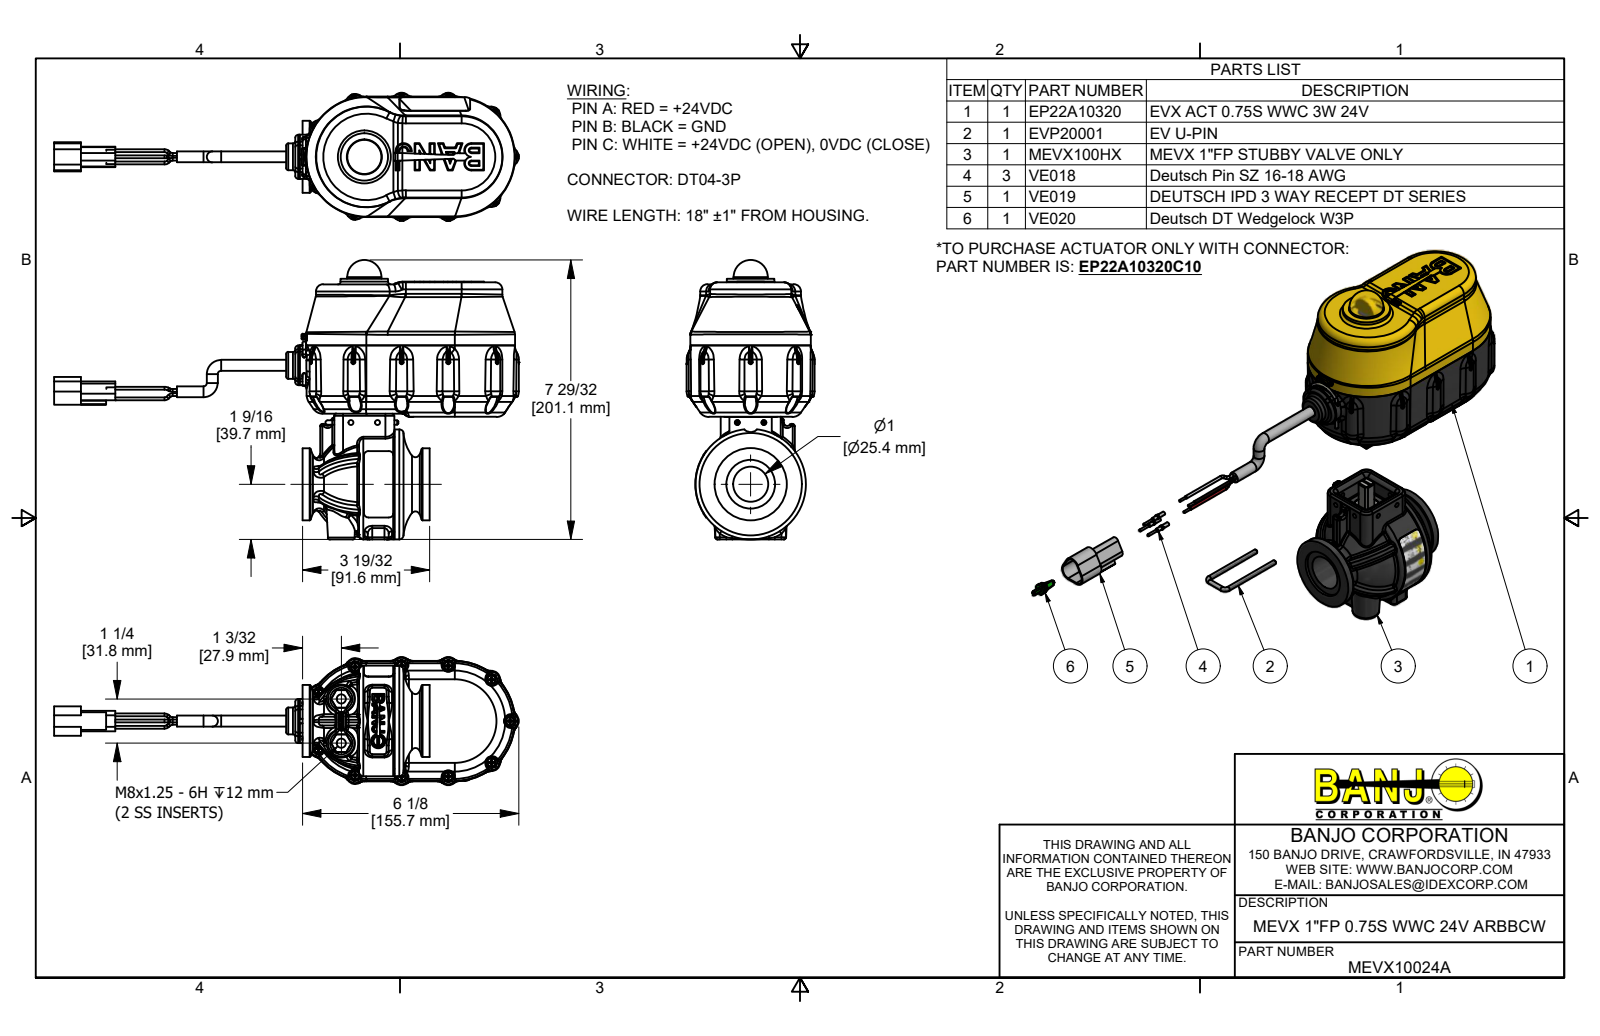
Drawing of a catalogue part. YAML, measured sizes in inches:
part_name: "MEVX10024A; EVP20001; MEVX100HX; MEVPS10254H (+8 more)"
step_written_by: "Autodesk Inventor 2019 (AUTOMOTIVE_DESIGN)"
units: inches
bodies: {solids: 89, faces: 11108, planar: 3083, cylindrical: 3143, other: 4882}
overall_size: [13.165, 7.916, 3.63]
volume: 45.79
surface_area: 545.2
round_holes:
  - {diameter: 0.095, count: 11}
  - {diameter: 0.15, count: 11}
  - {diameter: 0.08, count: 7}
  - {diameter: 0.107, count: 4}
  - {diameter: 0.126, count: 4}
  - {diameter: 0.135, count: 4}
  - {diameter: 0.136, count: 4}
  - {diameter: 0.148, count: 4}
  - {diameter: 0.15, count: 4}
  - {diameter: 0.17, count: 4}
  - {diameter: 0.02, count: 3}
  - {diameter: 0.06, count: 3}
round_bosses_or_shafts:
  - {diameter: 0.25, count: 17}
  - {diameter: 0.08, count: 15}
  - {diameter: 0.14, count: 11}
  - {diameter: 0.108, count: 11}
  - {diameter: 0.085, count: 11}
  - {diameter: 0.058, count: 6}
  - {diameter: 0.27, count: 4}
  - {diameter: 0.219, count: 4}
partial_cylinders:
  - {radius: 0.013, count: 180}
  - {radius: 0.04, count: 145}
  - {radius: 0.01, count: 84}
  - {radius: 0.02, count: 75}
  - {radius: 0.005, count: 53}
  - {radius: 0.06, count: 46}
  - {radius: 0.03, count: 30}
  - {radius: 0.125, count: 29}
face_to_face_distances: [0.1, 2.565, 0.151, 0.211, 0.06, 1.896, 1.836, 1.685, 0.569, 0.629]
hole_center_spacings: [1.79, 0.33, 1.513, 2.849, 3.789, 0.665, 0.668, 0.75]
